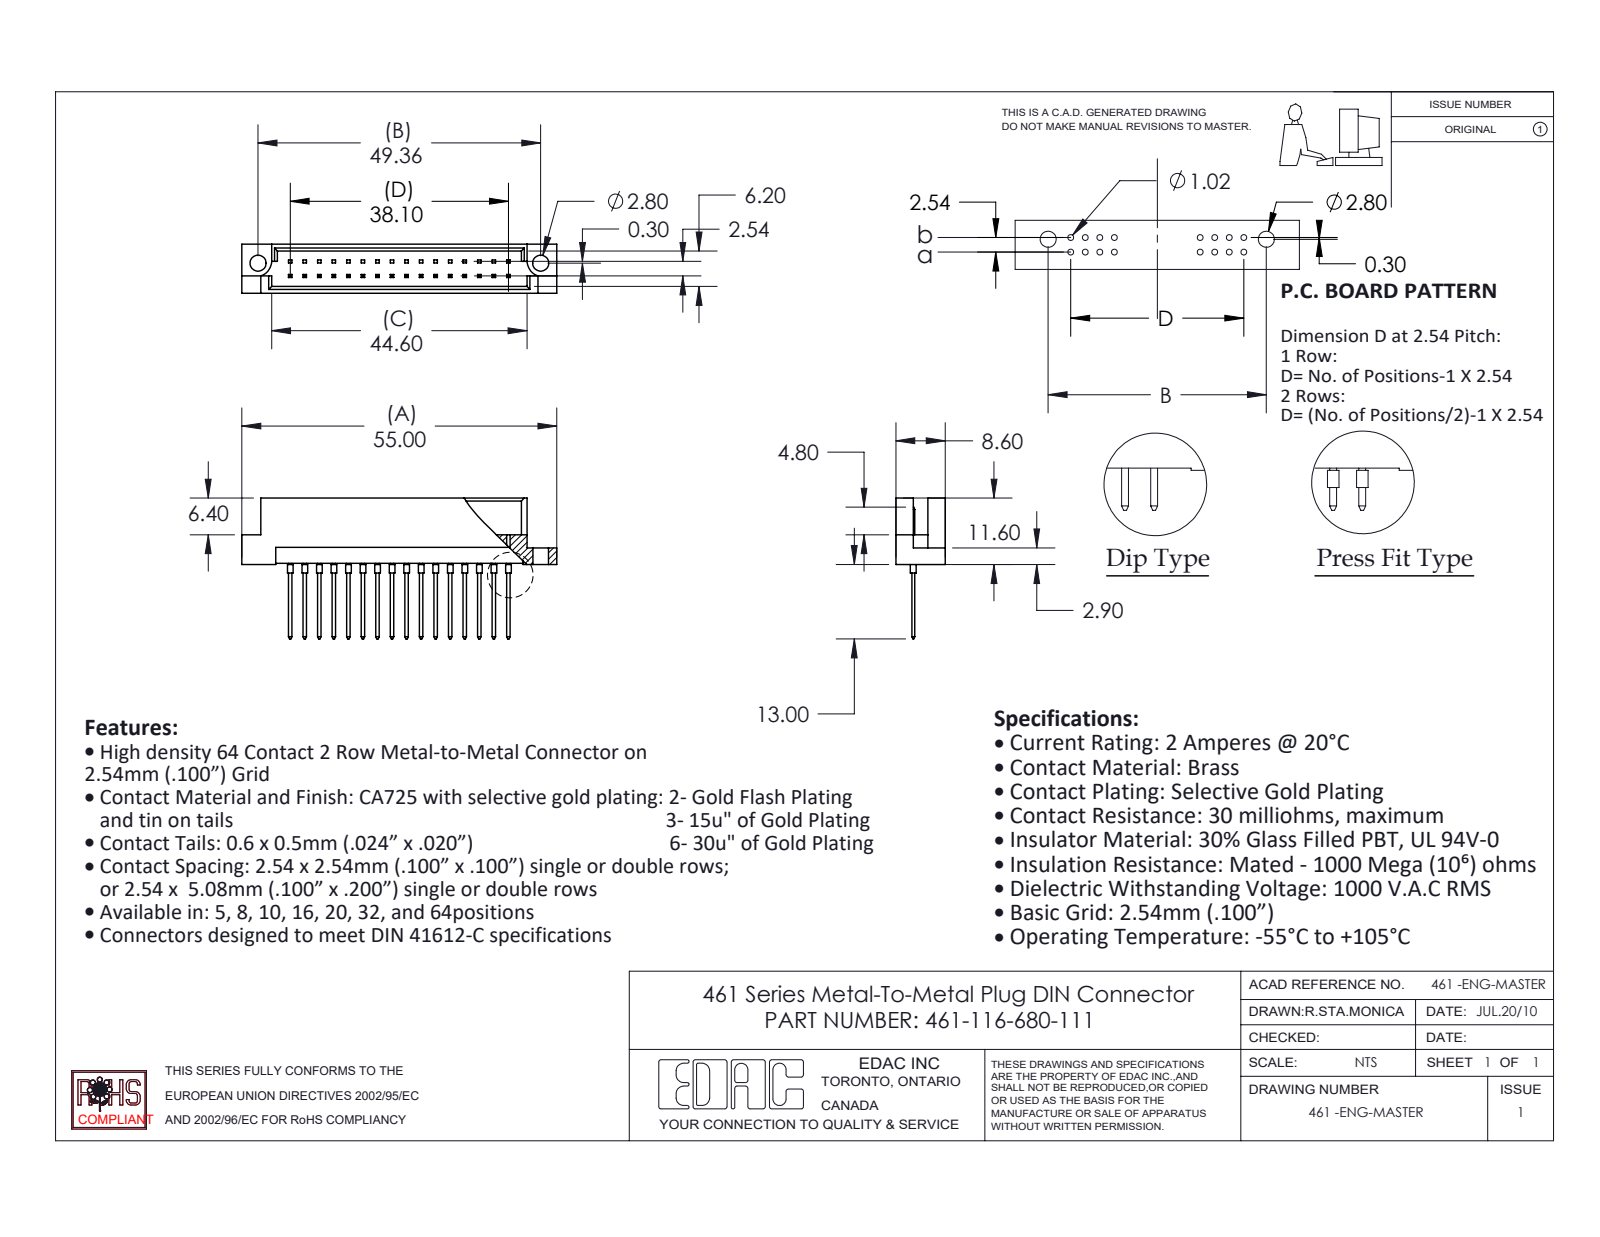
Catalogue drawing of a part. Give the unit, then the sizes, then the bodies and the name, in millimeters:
Units: millimetres
Overall size (bounding box): 55 × 24.6 × 8.6
Round holes (diameter × count): ⌀2.8 ×2
Round bosses / shafts (diameter × count): ⌀1 ×16
Partial cylindrical surfaces — rounded edges, fillets, slot ends (radius × count): R2.8 ×2
Main face-to-face distances: 1.2, 7.4, 8.6, 6.2, 2.54, 2.78, 5.82, 1.58, 4.62, 3.28
Hole centre spacings: 49.36
Volume: 2 774 mm³ · Surface area: 4 089 mm²
Bodies: 17 solids, 528 faces (490 planar, 38 cylindrical, 0 other)
Part name (STEP PRODUCT): 461-290_80; 461 Part_32; 461-116-680-111
STEP written by: SolidWorks 2020 (CONFIG_CONTROL_DESIGN)
